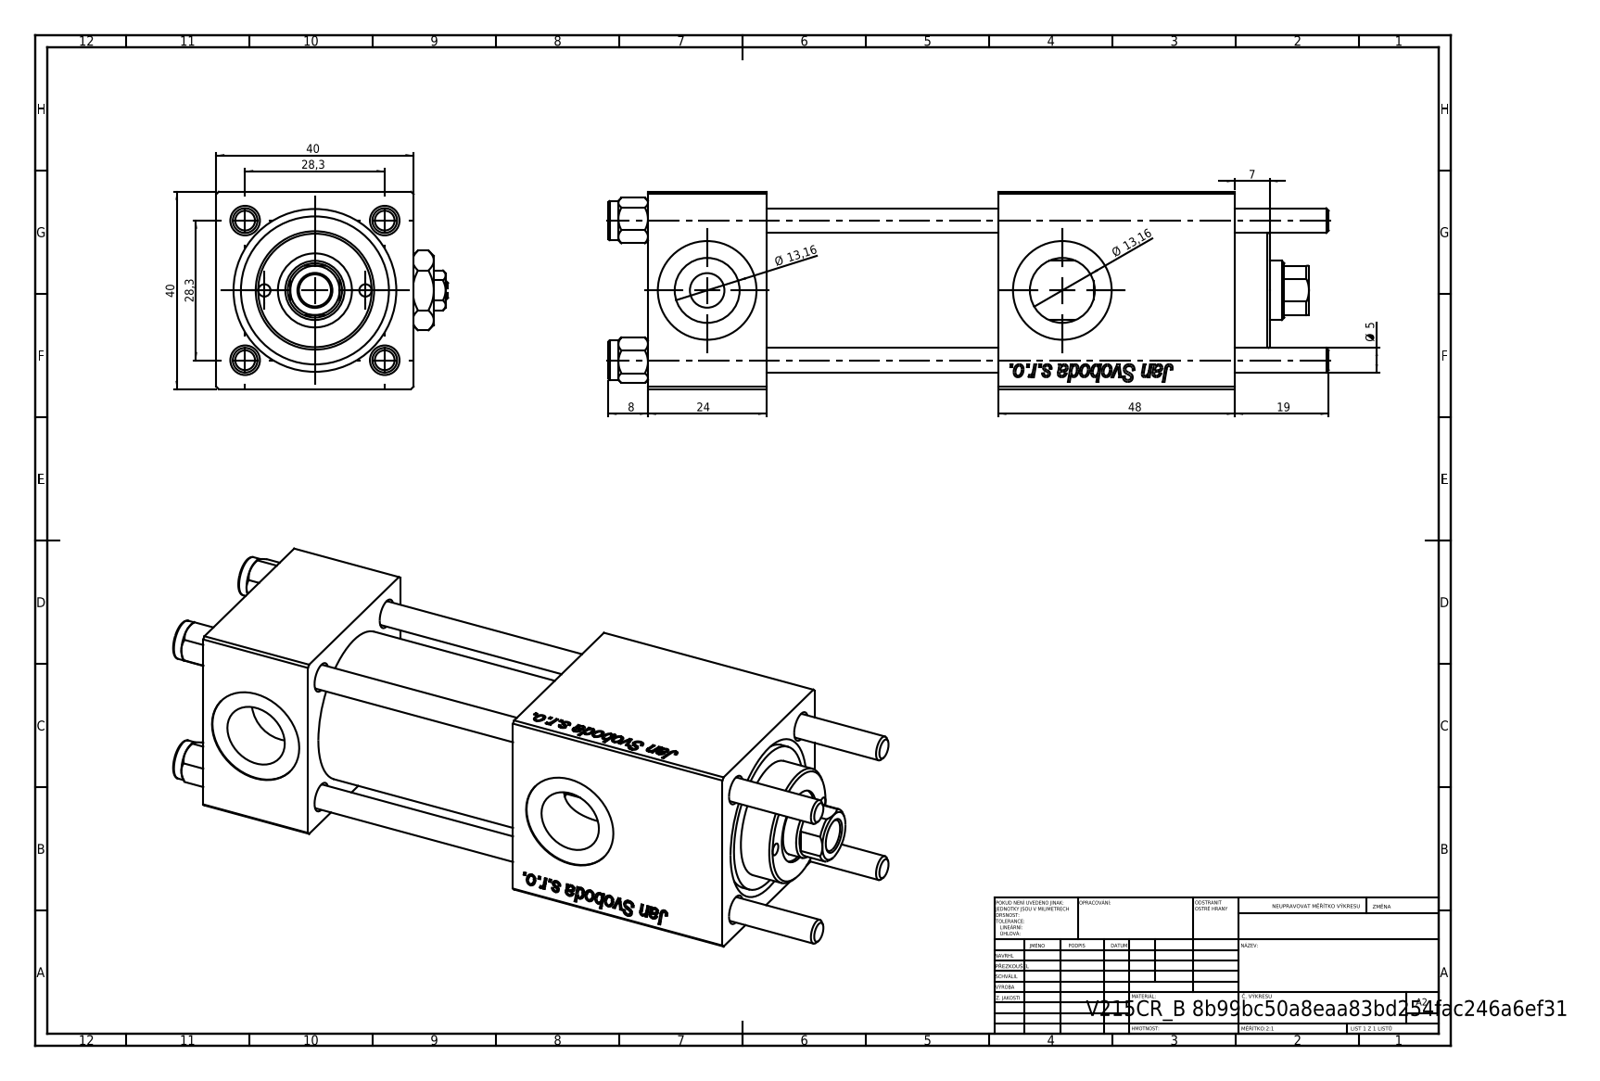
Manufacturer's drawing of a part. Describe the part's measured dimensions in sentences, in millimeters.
The part is named "NUT_M5_B; V215CR_B_TYCINKA; Zatka_pro_OIL_PORT; V215CR_VCP_B (+2 more)". Its 3-D file was written by "SolidWorks 2019 (CONFIG_CONTROL_DESIGN)". It is 12 solids with 1214 faces: 454 planar, 90 cylindrical and 670 other. Overall it measures 146 by 47 by 40 millimeters. Its volume is 144 013 cubic millimeters and its surface area 59 832 square millimeters. Round holes: 4 of diameter 5, 3 of diameter 20, 2 of diameter 2.5, 2 of diameter 7, 2 of diameter 13.16, 1 of diameter 6.5, 1 of diameter 12, 1 of diameter 15, 1 of diameter 25, 1 of diameter 30. Round bosses or shafts: 4 of diameter 8, 1 of diameter 31, 1 of diameter 24. Partial cylindrical surfaces (rounded edges, fillets, slot ends): 1 of radius 5.5. The main face-to-face distances are 40, 24, 90.3, 66.3, 119, 47, 71, 19.3, 95, 48. The hole center spacings are 14.68, 20.01, 28.21, 28.3, 10.25, 40.02, 20.5, 72.
